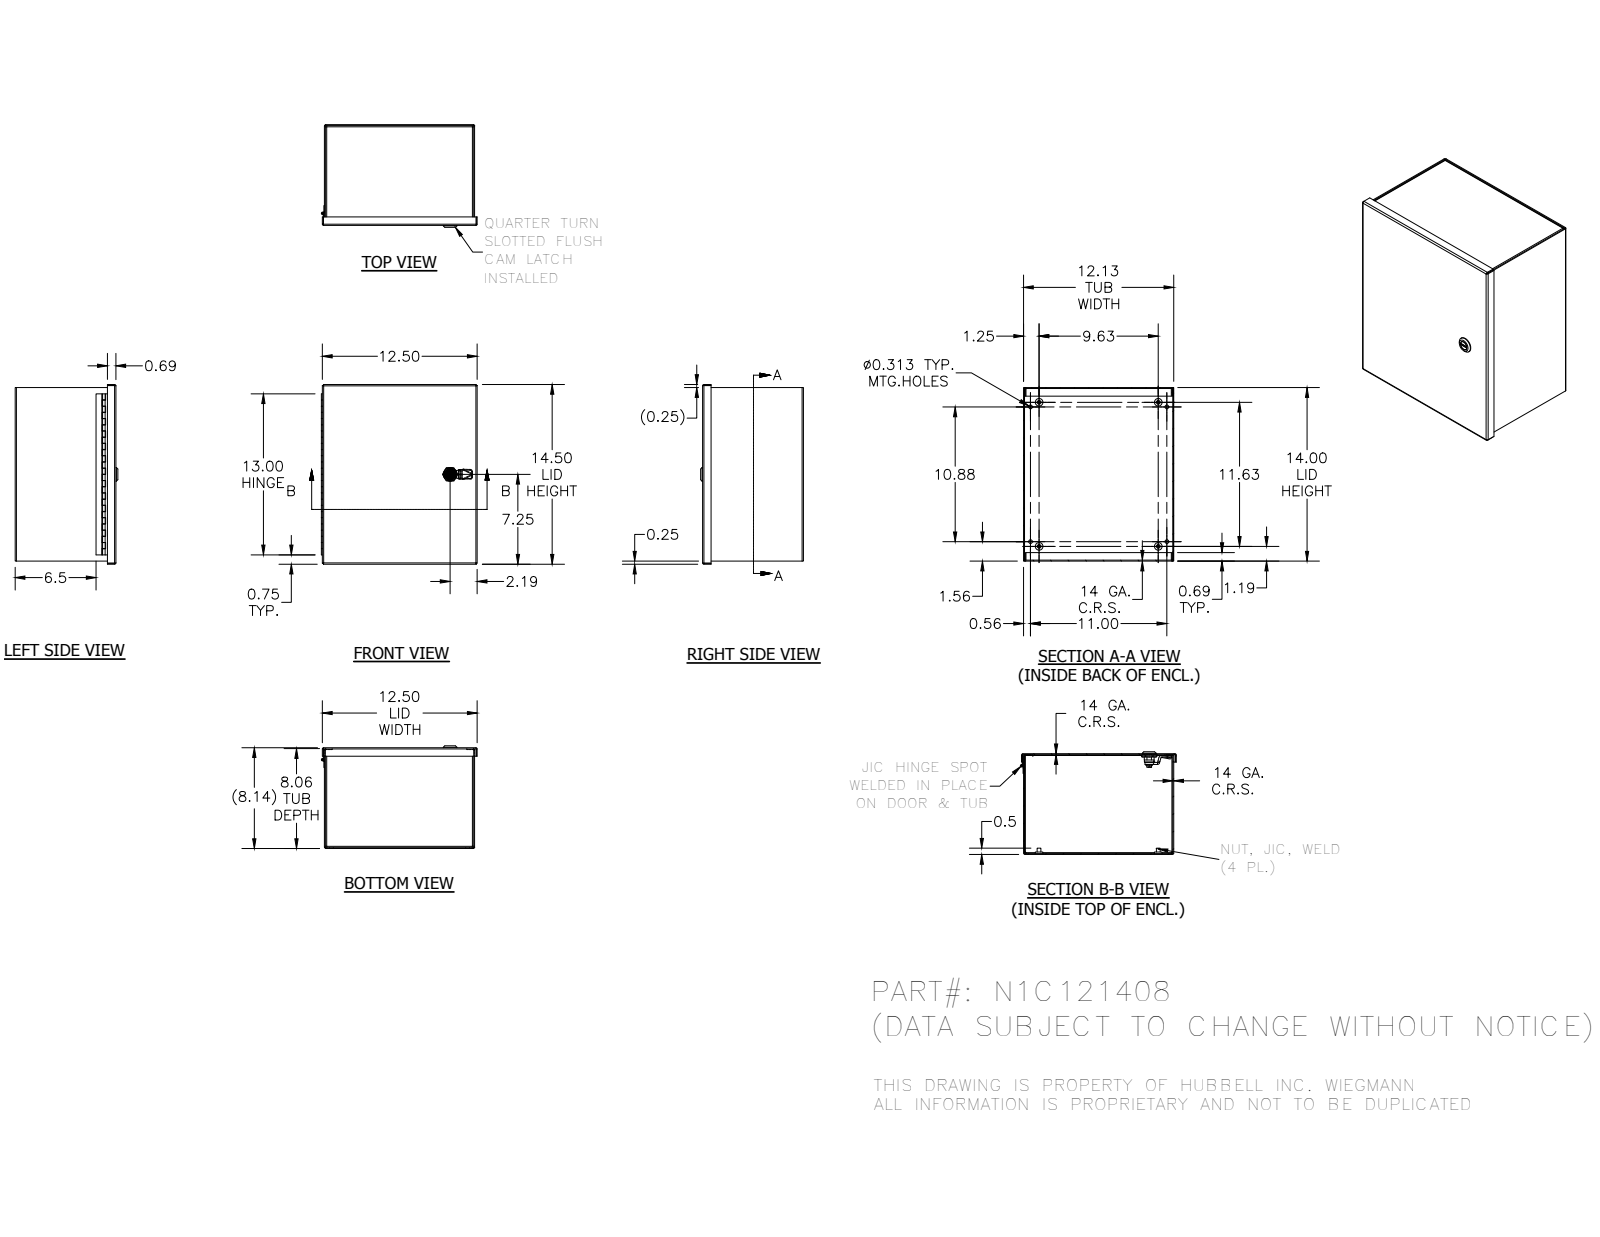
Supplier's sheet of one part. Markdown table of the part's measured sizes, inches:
| quantity | value |
| --- | --- |
| part name | N1C_SMALL; N1C1208TB; N1C121406BLR; HFW3513 (+8 more) |
| STEP written by | Autodesk Inventor 2012 (AUTOMOTIVE_DESIGN) |
| units | inches |
| bodies | 19 solids, 735 faces (423 planar, 230 cylindrical, 82 other) |
| overall size | 14.5 × 12.584 × 8.294 |
| volume | 61.18 in³ |
| surface area | 1 689 in² |
| round holes (diameter × count) | 0.156 × 4, 0.313 × 4, 0.116 × 1, 0.197 × 1, 0.315 × 1, 0.394 × 1, 0.402 × 1, 0.634 × 1, 0.802 × 1 |
| round bosses / shafts (diameter × count) | 0.625 × 4, 0.3 × 4, 1.102 × 1, 0.866 × 1, 0.78 × 1, 0.63 × 1, 0.598 × 1, 0.531 × 1 |
| partial cylindrical surfaces (radius × count) | 0.012 × 30, 0.031 × 16, 0.105 × 16, 0.02 × 10, 0.157 × 4, 0.016 × 3, 0.039 × 1, 0.173 × 1 |
| main face-to-face distances | 0.074, 8.063, 7.989, 13.926, 12.051, 8.137, 11.977, 14, 13.852, 12.125 |
| hole center spacings | 0.783, 10.319, 11.271, 15.261, 5.619, 5.858, 9.625, 10.626 |
